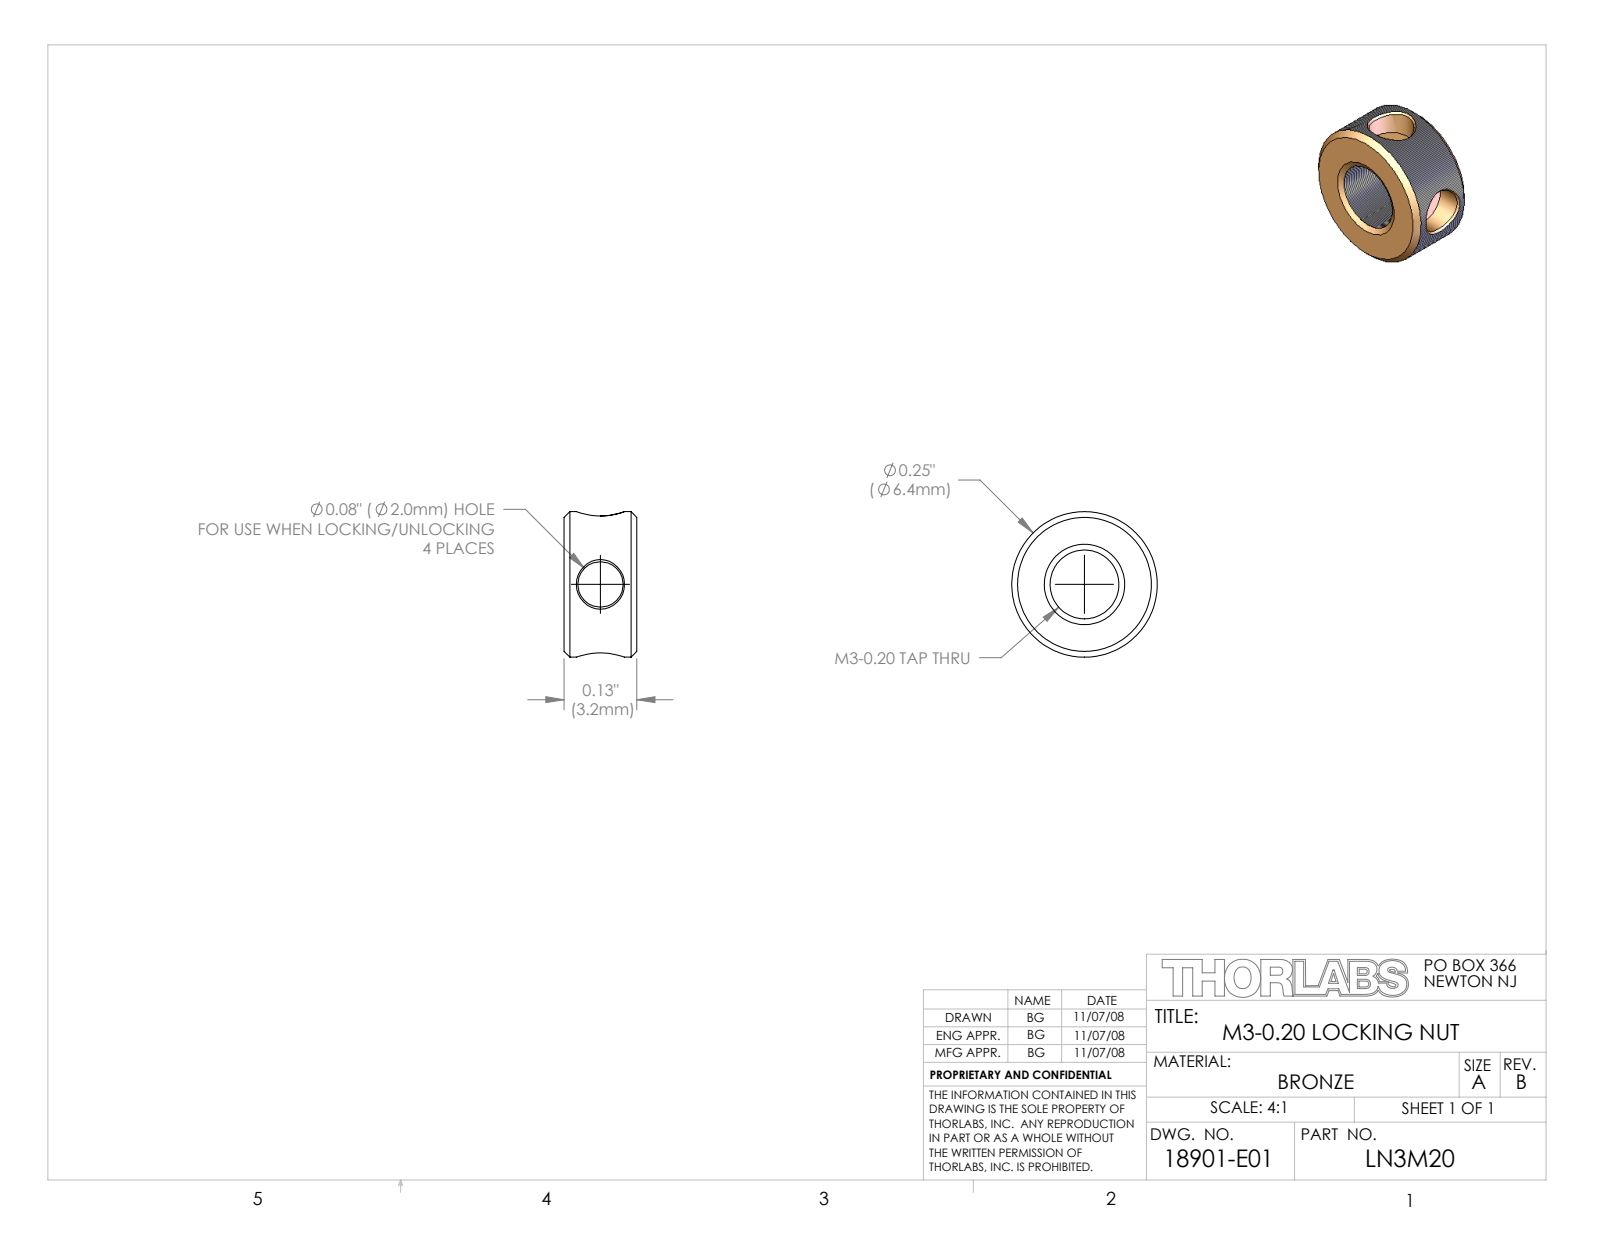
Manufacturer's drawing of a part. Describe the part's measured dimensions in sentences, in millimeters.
The part is named "18901-E0W". Its 3-D file was written by "SolidWorks 2007 (AUTOMOTIVE_DESIGN)". It is 1 solid with 34 faces: 6 planar, 12 cylindrical and 16 other. Overall it measures 6.35 by 6.35 by 3.17 millimeters. Its volume is 63 cubic millimeters and its surface area 159 square millimeters. Round holes: 2 of diameter 1.98, 1 of diameter 3. Round bosses or shafts: 1 of diameter 6.35. The main face-to-face distances are 3.18, 4.06.
